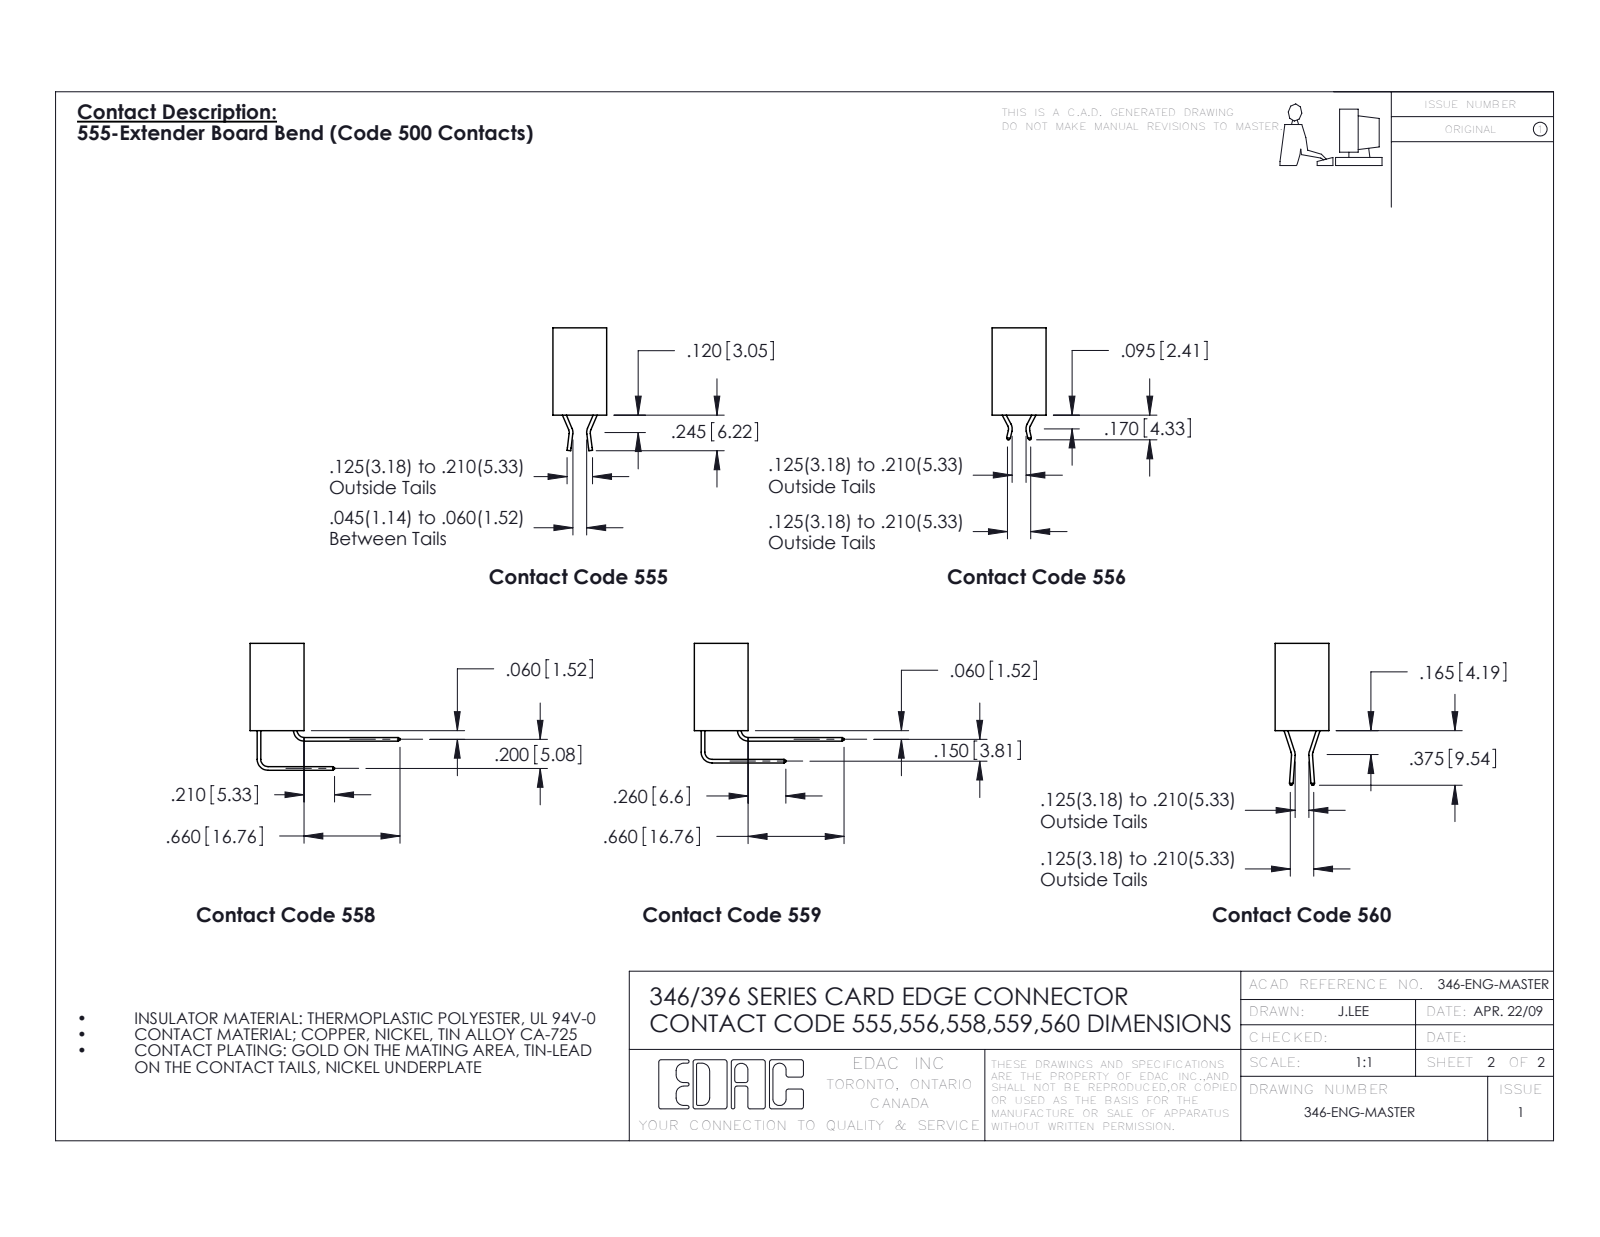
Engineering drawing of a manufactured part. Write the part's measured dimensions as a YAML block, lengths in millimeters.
part_name: "396-027-559-101; 346 Part_No Mounting Lugs; 345-292-001_558 559 Tail - 1"
step_written_by: "SolidWorks 2016 (CONFIG_CONTROL_DESIGN)"
units: millimeters
bodies: {solids: 28, faces: 1734, planar: 1206, cylindrical: 528, other: 0}
overall_size: [93, 26.2, 17.1]
volume: 9440
surface_area: 12250
round_holes:
  - {diameter: 1.6, count: 1}
partial_cylinders:
  - {radius: 0.2, count: 54}
  - {radius: 0.3, count: 22}
  - {radius: 0.2, count: 6}
  - {radius: 0.8, count: 6}
  - {radius: 0.7, count: 3}
  - {radius: 0.8, count: 2}
  - {radius: 1, count: 2}
  - {radius: 0.4, count: 1}
face_to_face_distances: [1.2, 8.2, 9.4, 6.4, 0.6, 1.8, 3.8, 5.6, 2.5, 4.4]
